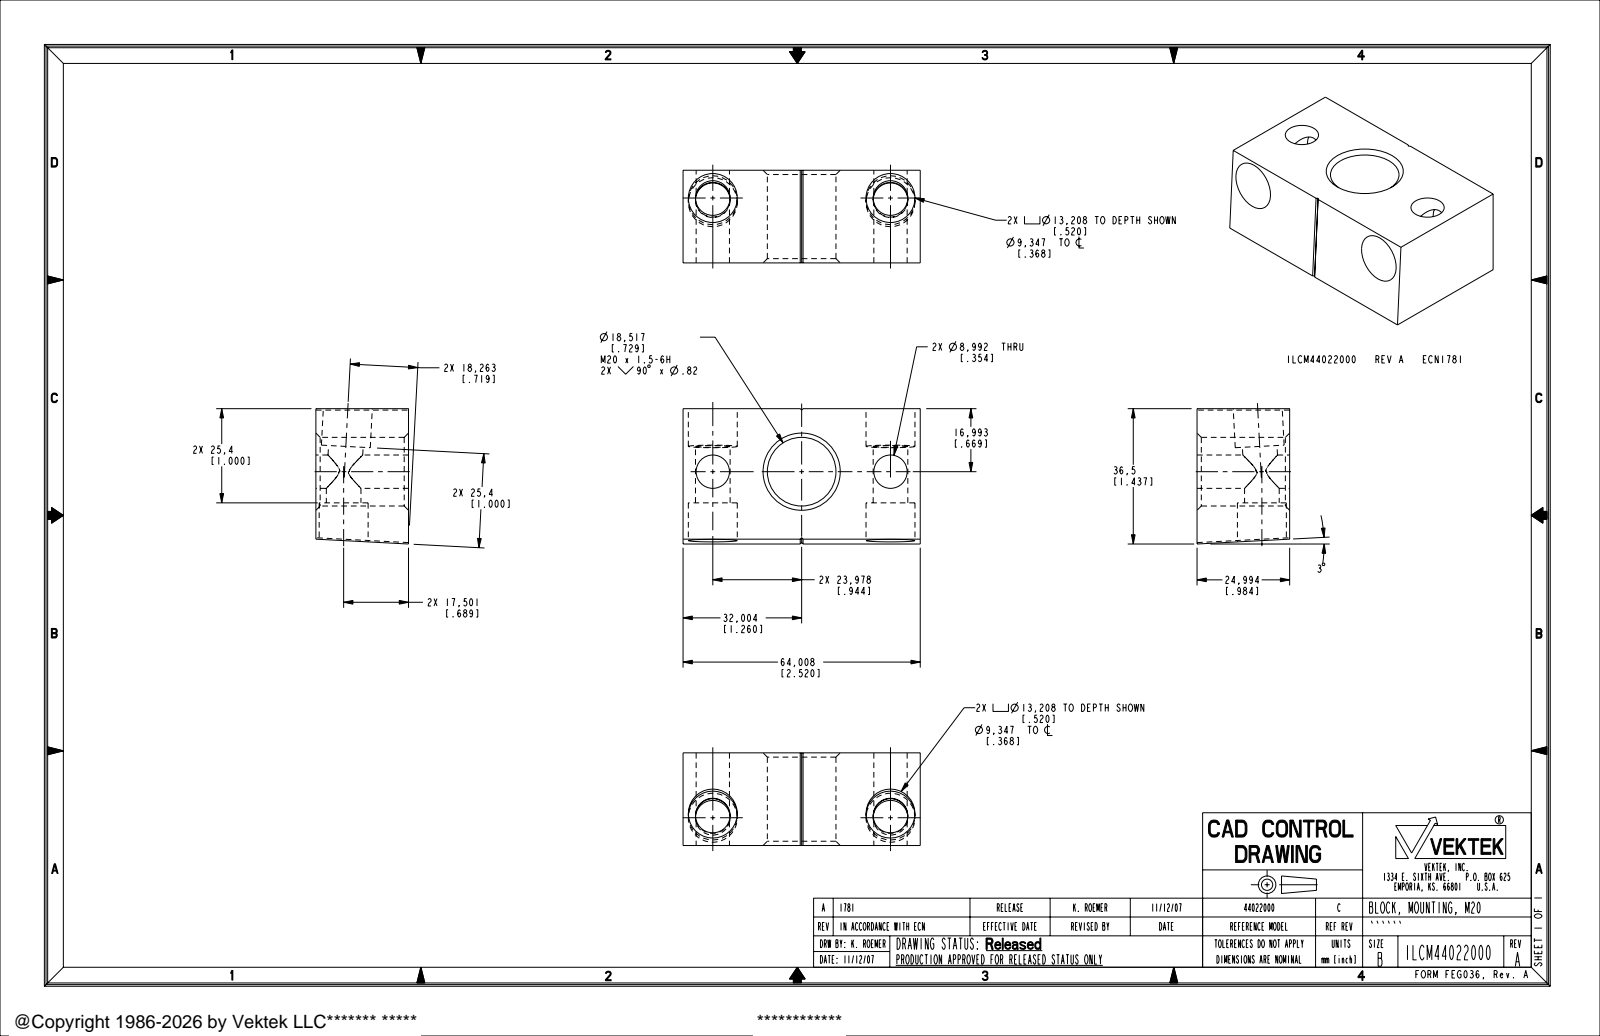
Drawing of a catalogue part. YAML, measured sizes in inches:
part_name: "ILCM44022000"
step_written_by: "PRO/ENGINEER BY PARAMETRIC TECHNOLOGY CORPORATION, 2005180 (AUTOMOTIVE_DESIGN_CC2)"
units: inches
bodies: {solids: 1, faces: 54, planar: 24, cylindrical: 26, other: 4}
overall_size: [2.52, 1.437, 0.984]
volume: 2.484
surface_area: 20.51
round_holes:
  - {diameter: 0.368, count: 4}
  - {diameter: 0.52, count: 4}
  - {diameter: 0.354, count: 2}
  - {diameter: 0.729, count: 1}
face_to_face_distances: [0.984, 2.52, 1, 1, 0.669, 0.331]
hole_center_spacings: [1.888, 0.944, 0.944]
